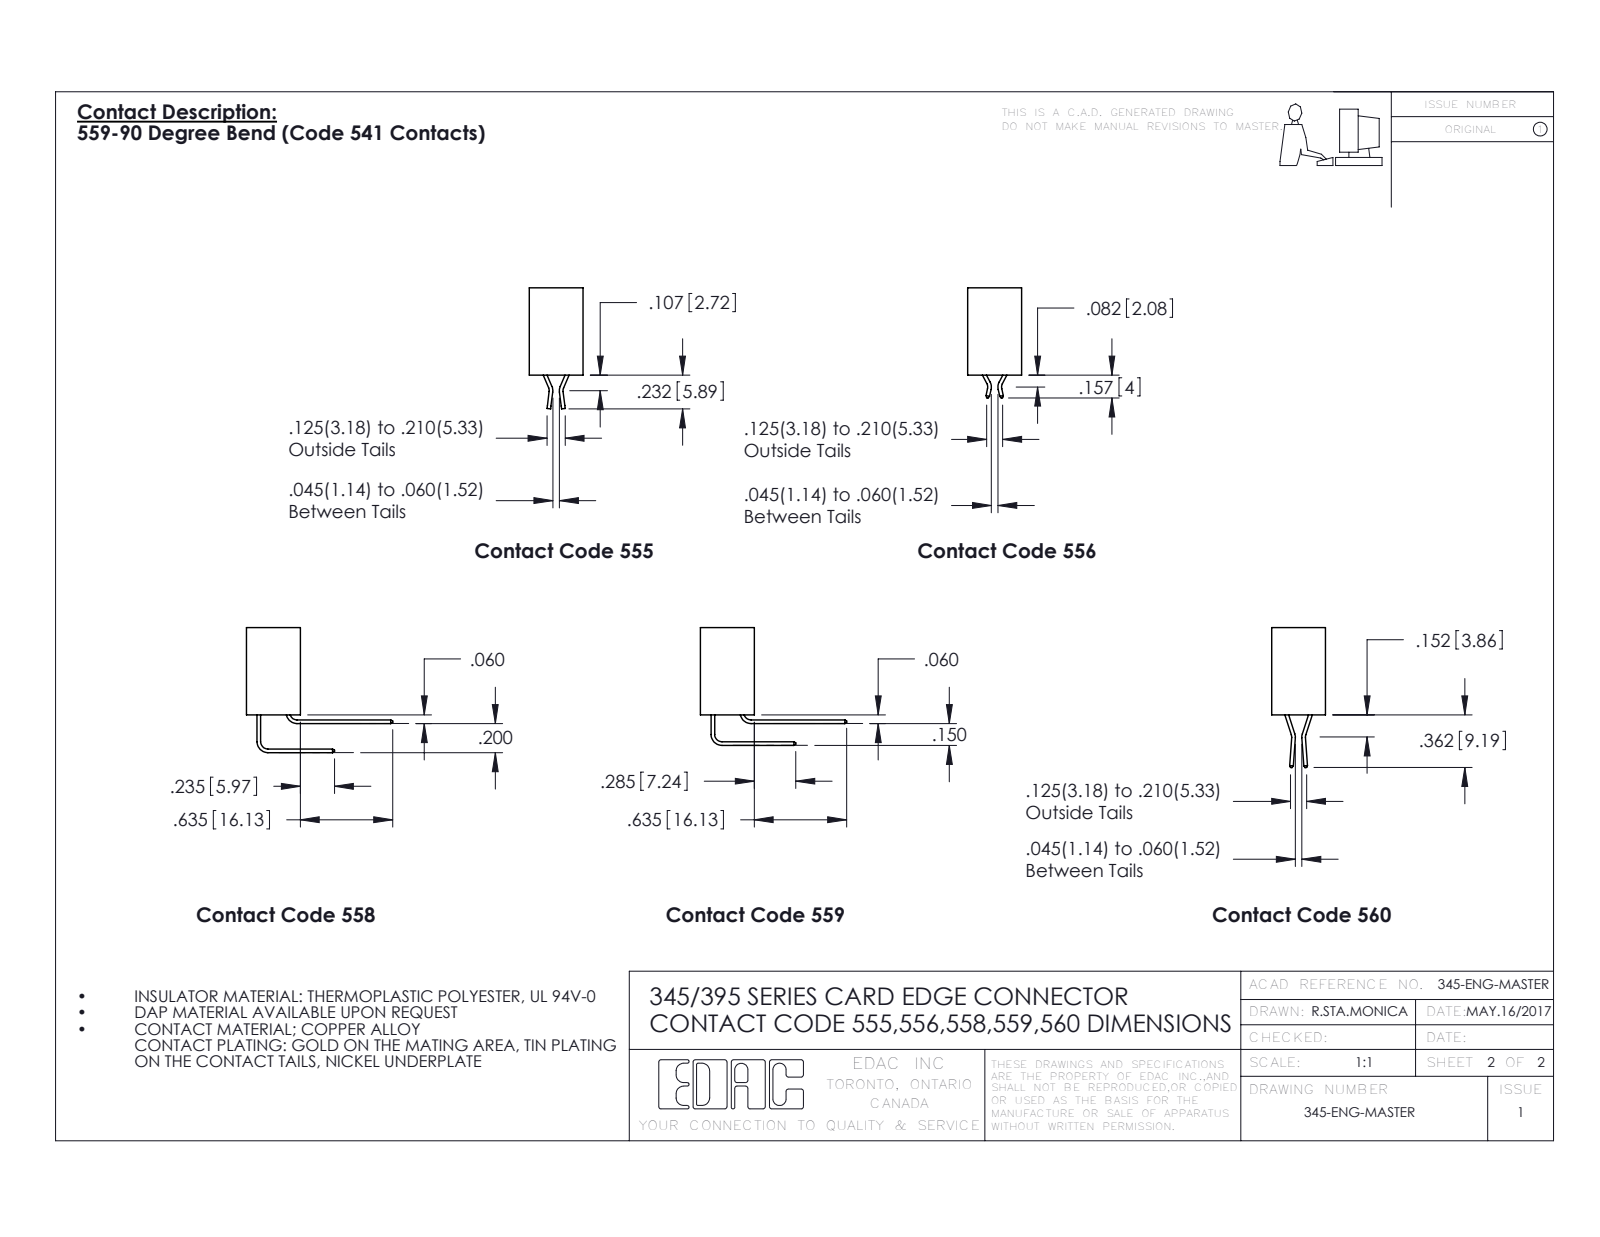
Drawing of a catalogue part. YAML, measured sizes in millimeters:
part_name: "345 Part_0.110 Offset - Side Mount; 345-292-001_558 559 Tail - 1; 395-020-559-412"
step_written_by: "SolidWorks 2016 (CONFIG_CONTROL_DESIGN)"
units: millimeters
bodies: {solids: 21, faces: 1330, planar: 924, cylindrical: 406, other: 0}
overall_size: [72, 25.5, 16.7]
volume: 6570
surface_area: 8755
round_holes:
  - {diameter: 3.3, count: 2}
  - {diameter: 1.6, count: 1}
partial_cylinders:
  - {radius: 0.2, count: 40}
  - {radius: 0.3, count: 22}
  - {radius: 0.2, count: 6}
  - {radius: 0.8, count: 6}
  - {radius: 0.7, count: 3}
  - {radius: 0.8, count: 2}
  - {radius: 1, count: 2}
  - {radius: 0.4, count: 1}
face_to_face_distances: [1.8, 7.6, 9.4, 5.1, 2.5, 6.9, 0.6, 5.7, 3.8, 15.2]
hole_center_spacings: [65.4]
